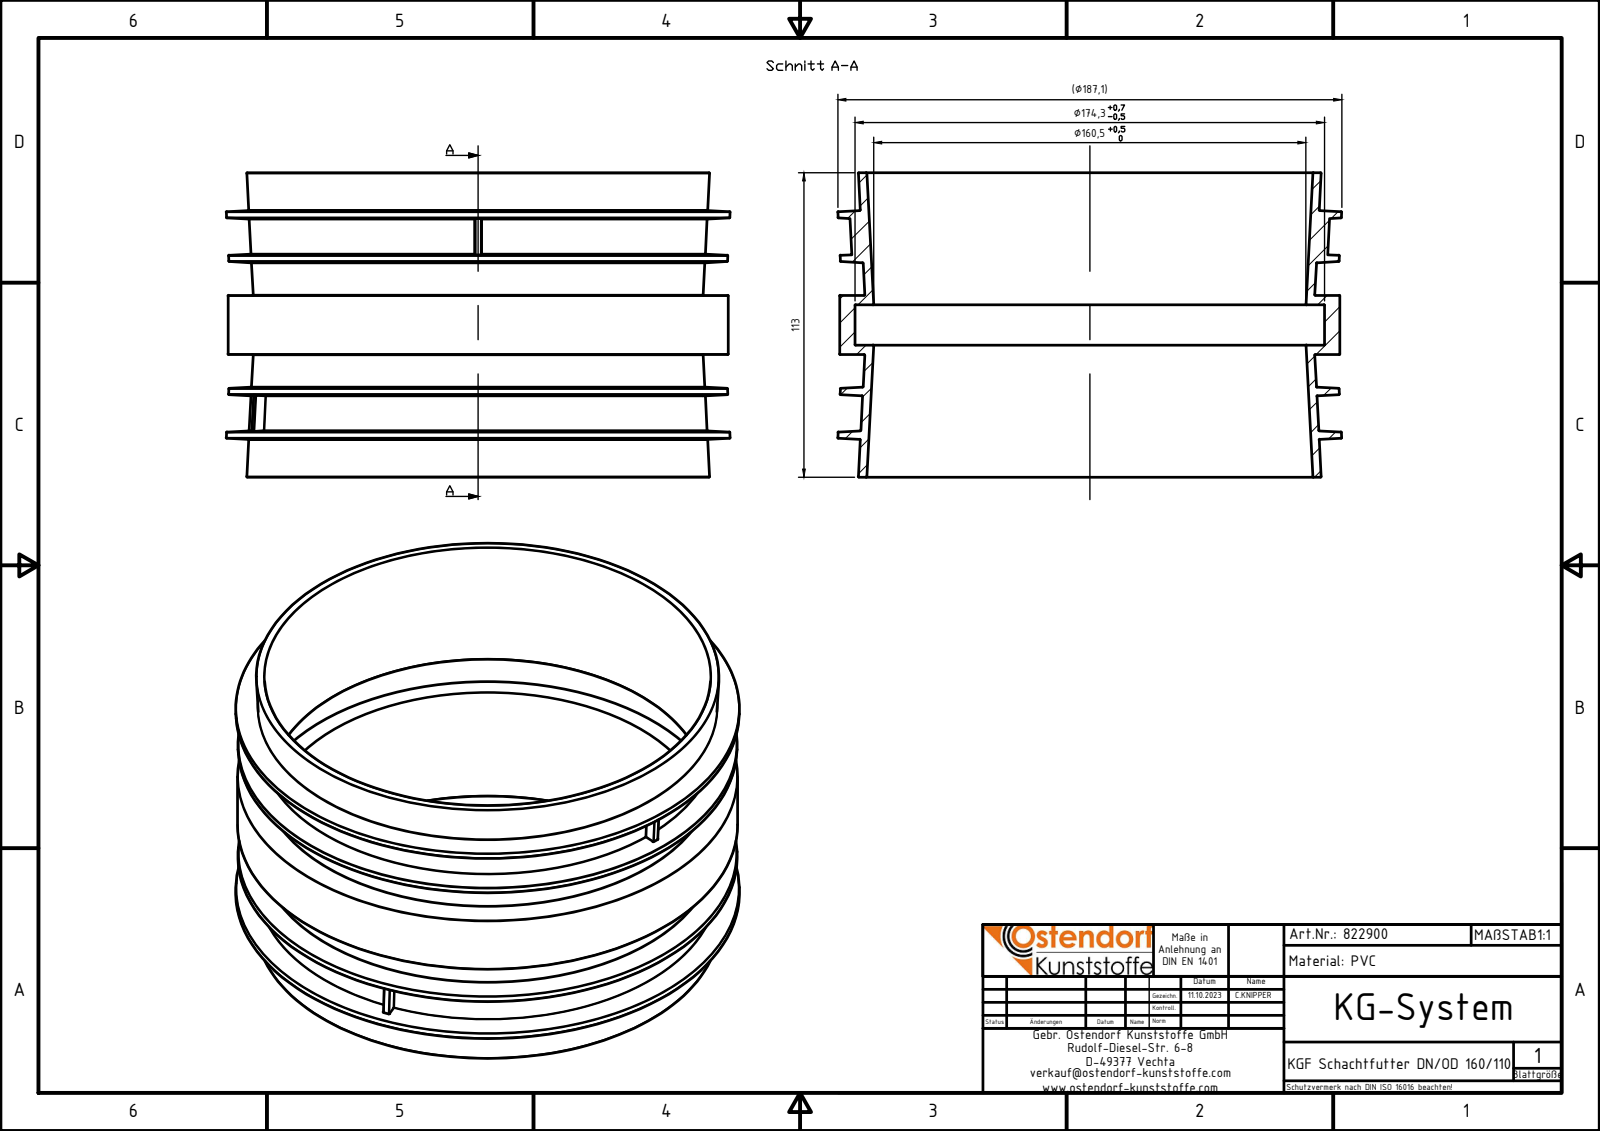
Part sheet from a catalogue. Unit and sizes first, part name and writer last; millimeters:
Units: millimetres
Overall size (bounding box): 187.08 × 187.08 × 113
Round holes (diameter × count): ⌀174.3 ×1
Round bosses / shafts (diameter × count): ⌀185.7 ×1
Partial cylindrical surfaces — rounded edges, fillets, slot ends (radius × count): R0.2 ×8
Main face-to-face distances: 3.5, 18.5, 22, 15, 45.5, 49, 64, 67.5, 113, 2.4
Volume: 295 373 mm³ · Surface area: 175 879 mm²
Bodies: 1 solid, 138 faces (18 planar, 10 cylindrical, 110 other)
Part name (STEP PRODUCT): 822900z
STEP written by: Autodesk Inventor 2024 (AUTOMOTIVE_DESIGN)
